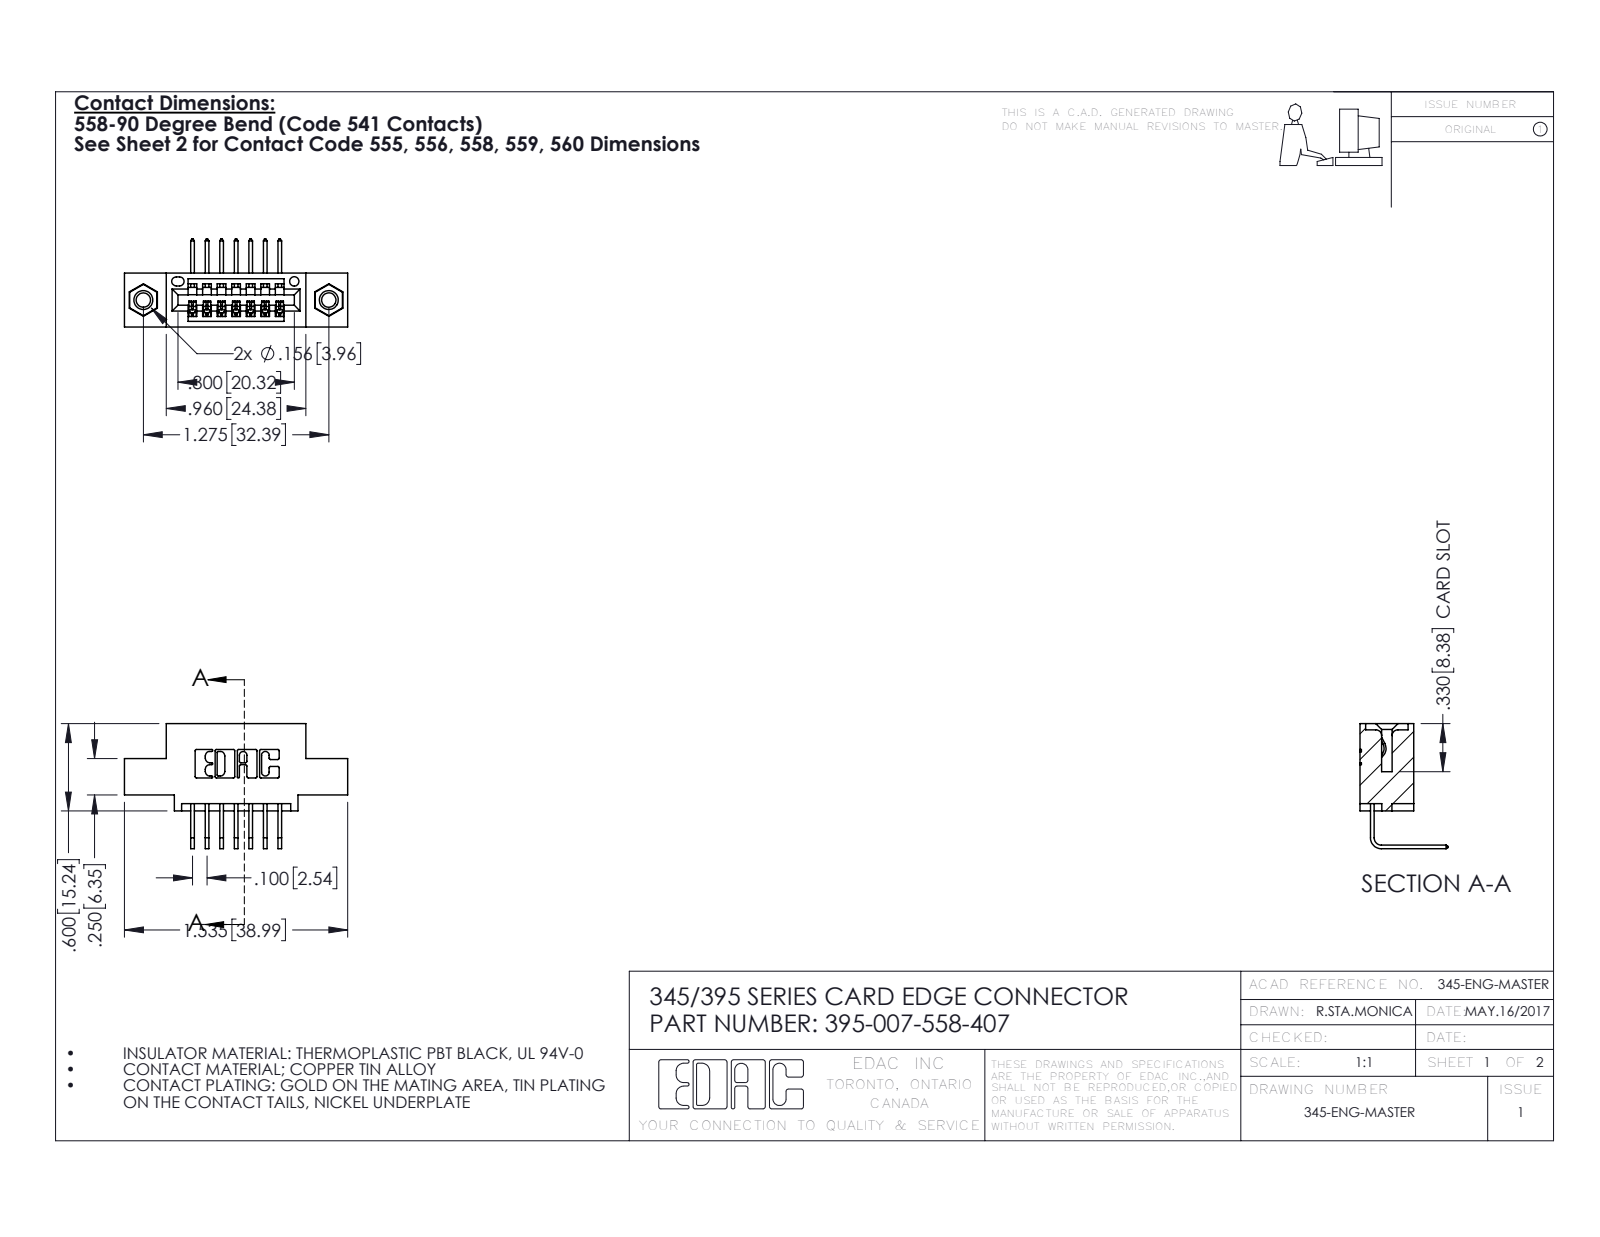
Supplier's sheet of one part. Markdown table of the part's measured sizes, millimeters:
| quantity | value |
| --- | --- |
| part name | 345 Part_0.110 Offset - 0.156 Dia-TI; 395-007-558-407; 345-250-001_345-250-005-103; 345-292-001_558 Tail - 2 |
| STEP written by | SolidWorks 2016 (CONFIG_CONTROL_DESIGN) |
| units | millimeters |
| bodies | 10 solids, 610 faces (410 planar, 184 cylindrical, 16 other) |
| overall size | 39 × 21.8 × 15.4 |
| volume | 3 360 mm³ |
| surface area | 4 232 mm² |
| round holes (diameter × count) | 2.5 × 2, 3.2 × 2, 4 × 2, 1.6 × 1 |
| round bosses / shafts (diameter × count) | 3.9 × 2 |
| partial cylindrical surfaces (radius × count) | 0.3 × 22, 0.2 × 14, 0.2 × 6, 0.8 × 6, 0.7 × 3, 0.8 × 2, 1 × 2, 0.4 × 1 |
| main face-to-face distances | 5.1, 9.4, 1.8, 7.6, 2.5, 7.6, 2.5, 6.9, 0.6, 4.1 |
| hole center spacings | 6.9, 26.5, 32.4 |
